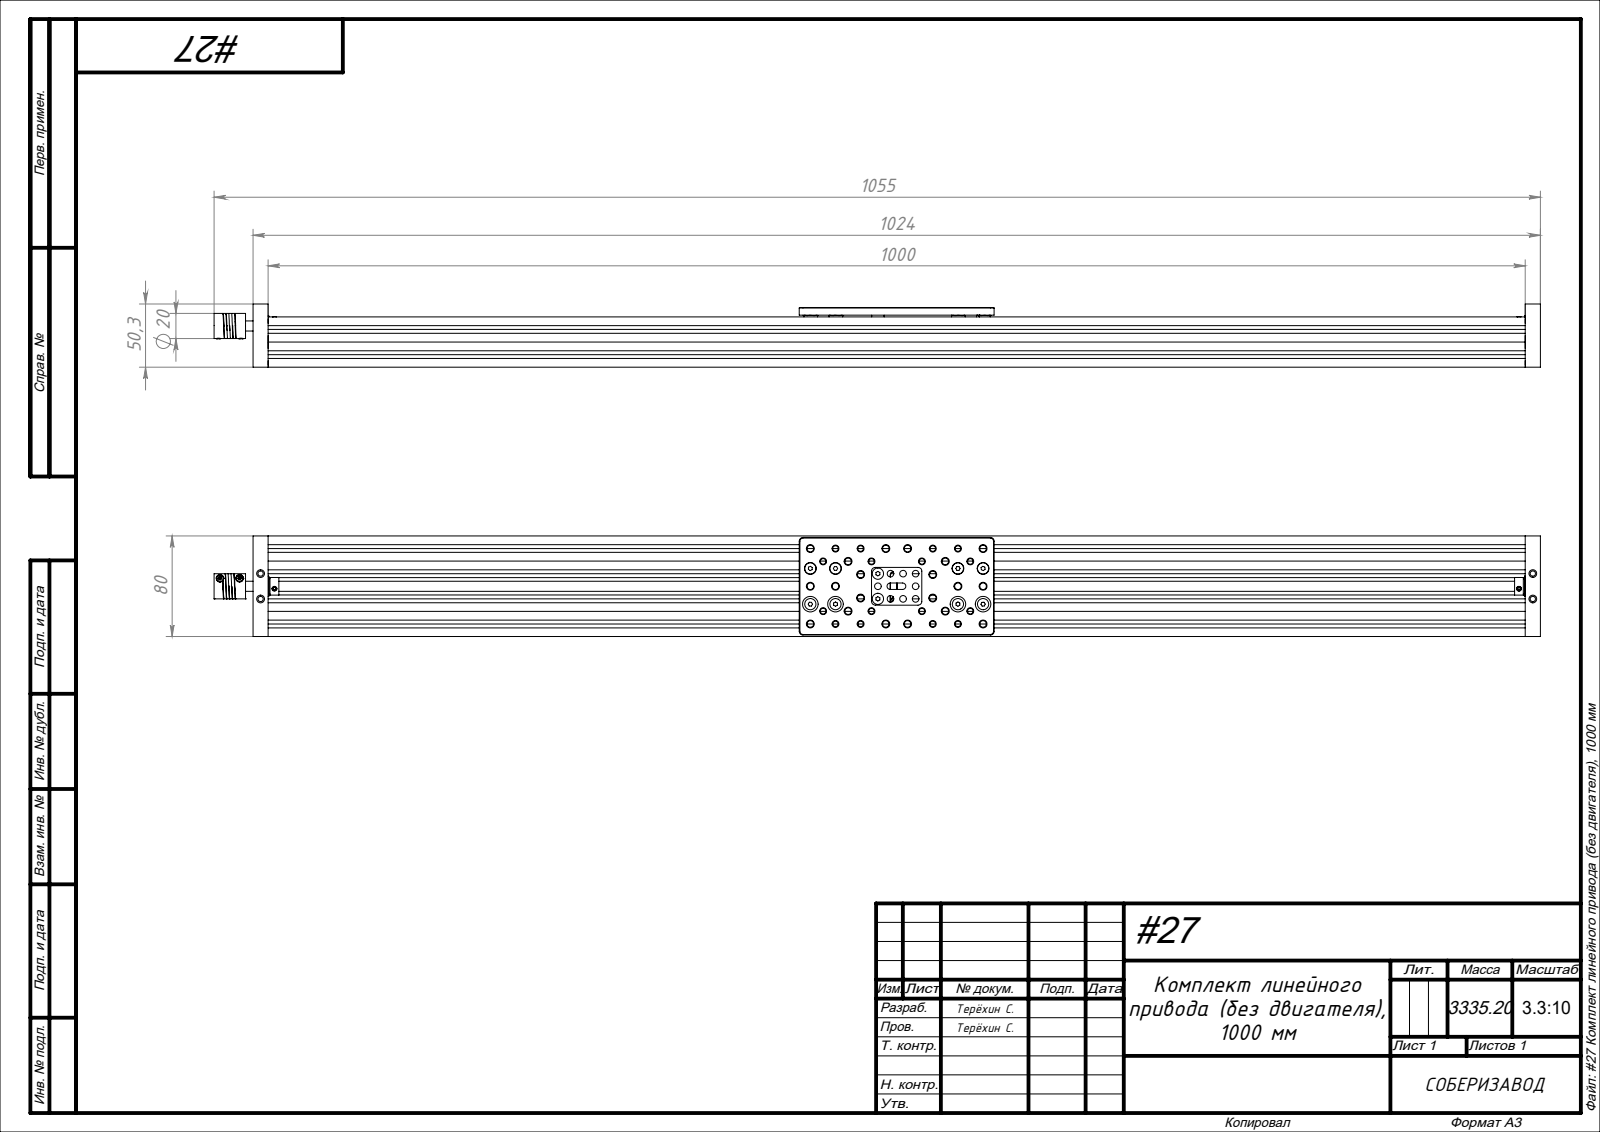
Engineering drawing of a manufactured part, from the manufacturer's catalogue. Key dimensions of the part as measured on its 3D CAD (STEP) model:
Part name (STEP PRODUCT): A247 Концевой кронштейн 50х80 (С-профиля)_00; A229 Самоконтрящаяся гайка M5_00; Комплект двойной портальной пластины для С профиля 77x155_00; A225 Гибкая муфта O 6,35 O 8_00 (+8 more)
STEP written by: SolidWorks 2021 (AUTOMOTIVE_DESIGN)
Units: millimetres
Bodies: 171 solids, 4603 faces (1282 planar, 1432 cylindrical, 1889 other)
Overall size (bounding box): 1055 × 80 × 50.3
Volume: 1 141 000 mm³ · Surface area: 937 376 mm²
Round holes (diameter × count): ⌀5.3 ×44, ⌀4.5 ×16, ⌀5 ×16, ⌀4.2 ×11, ⌀4.13 ×10, ⌀5.15 ×10, ⌀6.09 ×8, ⌀7.8 ×8, ⌀8.4 ×8, ⌀8.65 ×8, ⌀5.2 ×4, ⌀7.2 ×4
Round bosses / shafts (diameter × count): ⌀8 ×14, ⌀7.83 ×10, ⌀15.23 ×8, ⌀8.95 ×8, ⌀8.64 ×8, ⌀7 ×8, ⌀6.27 ×8, ⌀6 ×8
Partial cylindrical surfaces — rounded edges, fillets, slot ends (radius × count): R0.25 ×100, R0.2 ×86, R2 ×48, R1 ×40, R0.3 ×30, R1.4 ×20, R3 ×8, R1.5 ×6
Main face-to-face distances: 14.14, 28.28, 20, 1.8, 12, 6, 12.34, 14, 42.42, 2.83
Hole centre spacings: 20, 15.6, 10, 17.87, 22.39, 53.91, 6.21, 20.03
